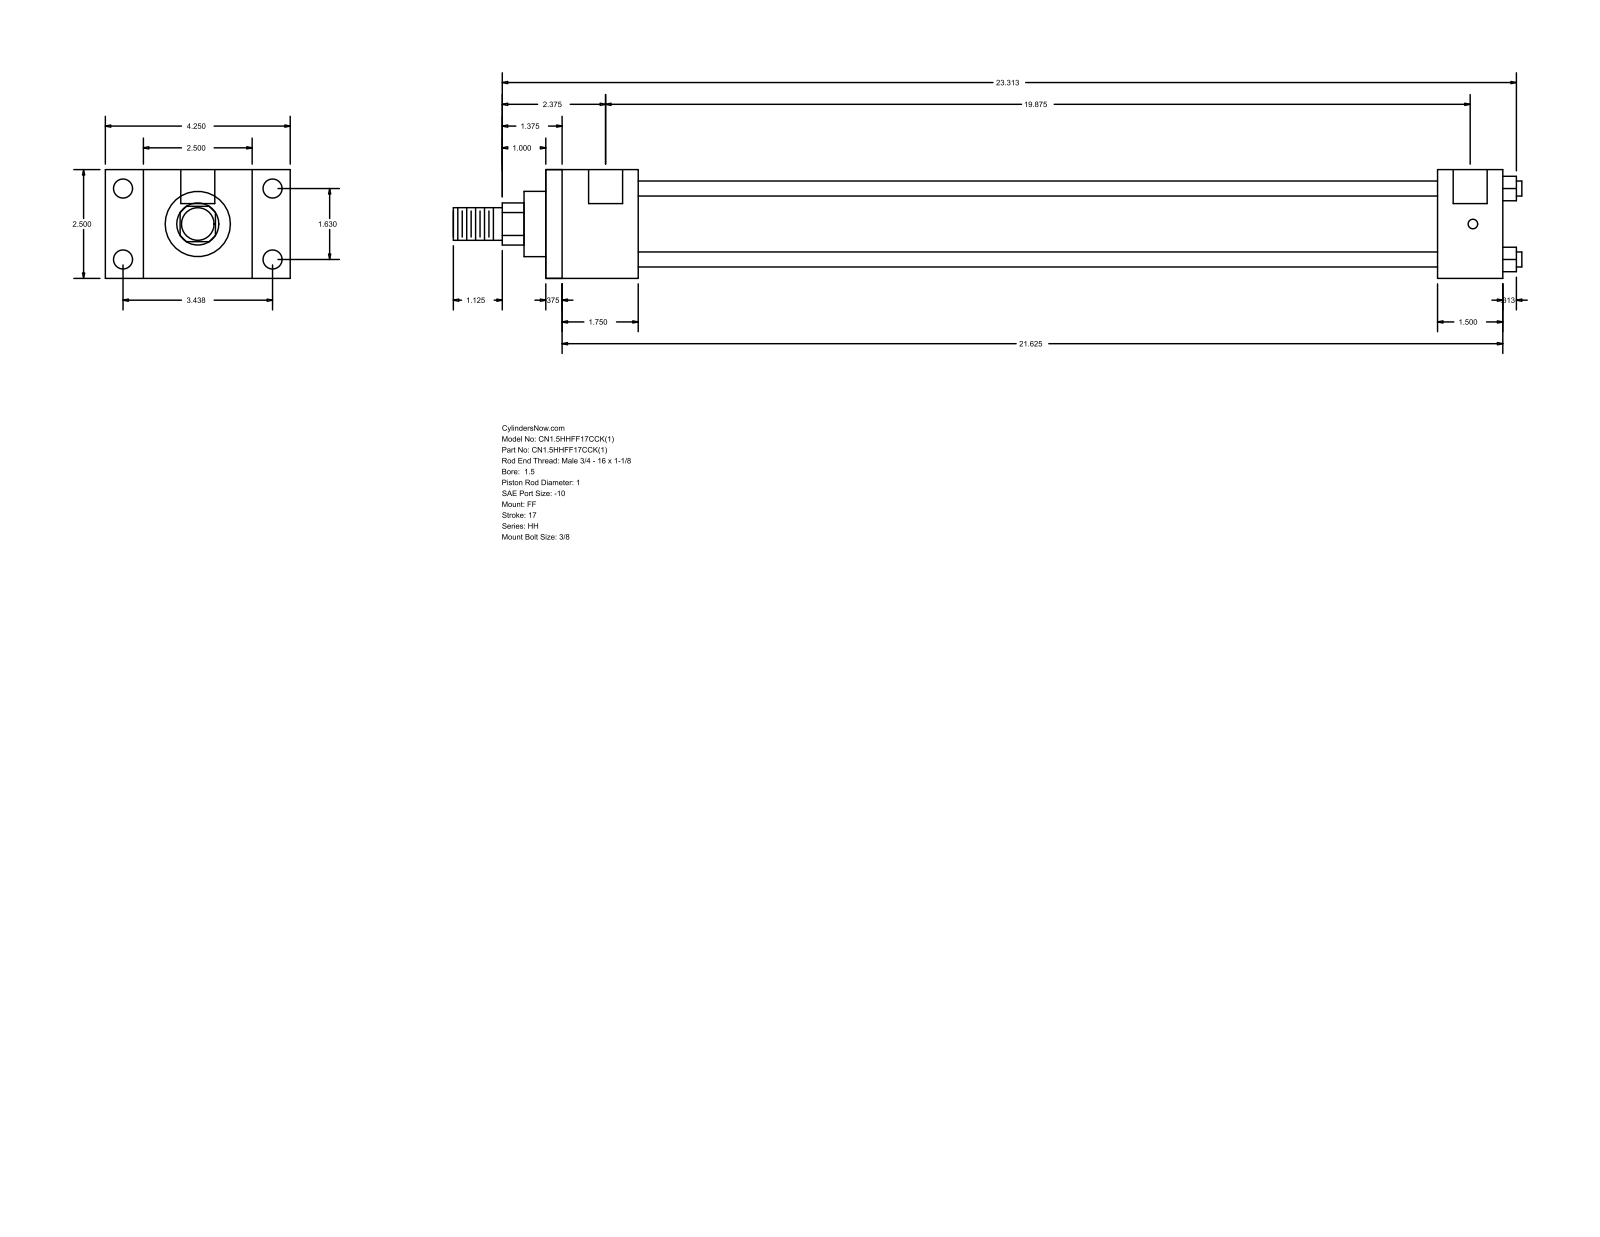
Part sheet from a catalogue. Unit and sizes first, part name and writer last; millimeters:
Units: millimetres
Overall size (bounding box): 623.89 × 107.95 × 63.5
Round holes (diameter × count): ⌀5.56 ×4, ⌀11.13 ×4, ⌀19.84 ×2
Round bosses / shafts (diameter × count): ⌀8.76 ×4, ⌀44.45 ×1, ⌀38.1 ×1, ⌀25.4 ×1, ⌀19.05 ×1
Partial cylindrical surfaces — rounded edges, fillets, slot ends (radius × count): R12.29 ×1
Main face-to-face distances: 63.5, 558.8, 9.52, 549.28, 38.1, 53.98, 44.46, 504.82, 520.7, 511.18
Hole centre spacings: 1.59, 41.4, 87.32, 96.64, 506.41, 508, 504.82
Bodies: 0 solids, 92 faces (64 planar, 28 cylindrical, 0 other)
Part name (STEP PRODUCT): HH_FF__0150_1
STEP written by: GSSL Pune (CONFIG_CONTROL_DESIGN)
